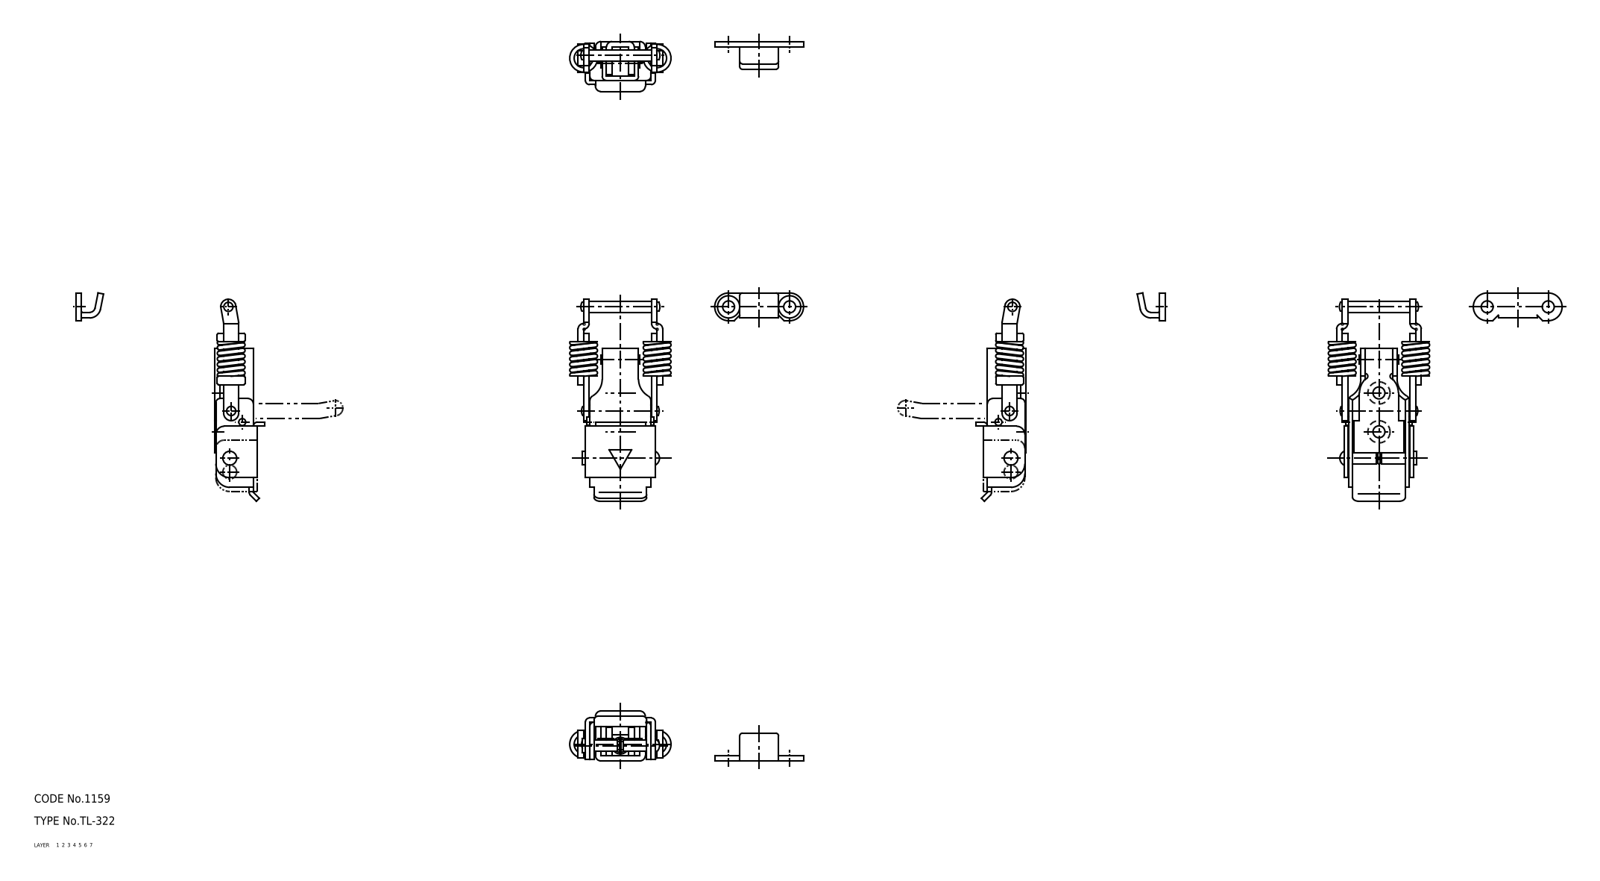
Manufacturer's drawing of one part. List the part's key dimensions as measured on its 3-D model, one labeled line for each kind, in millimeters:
Part name (STEP PRODUCT): arm_C_mr; spring; shaft_A; shaft_B (+8 more)
STEP written by: CADfix (AUTOMOTIVE_DESIGN)
Units: millimetres
Bodies: 14 solids, 321 faces (0 planar, 0 cylindrical, 321 other)
Overall size (bounding box): 75 × 36.25 × 18
Volume: 10 069 mm³ · Surface area: 14 973 mm²
